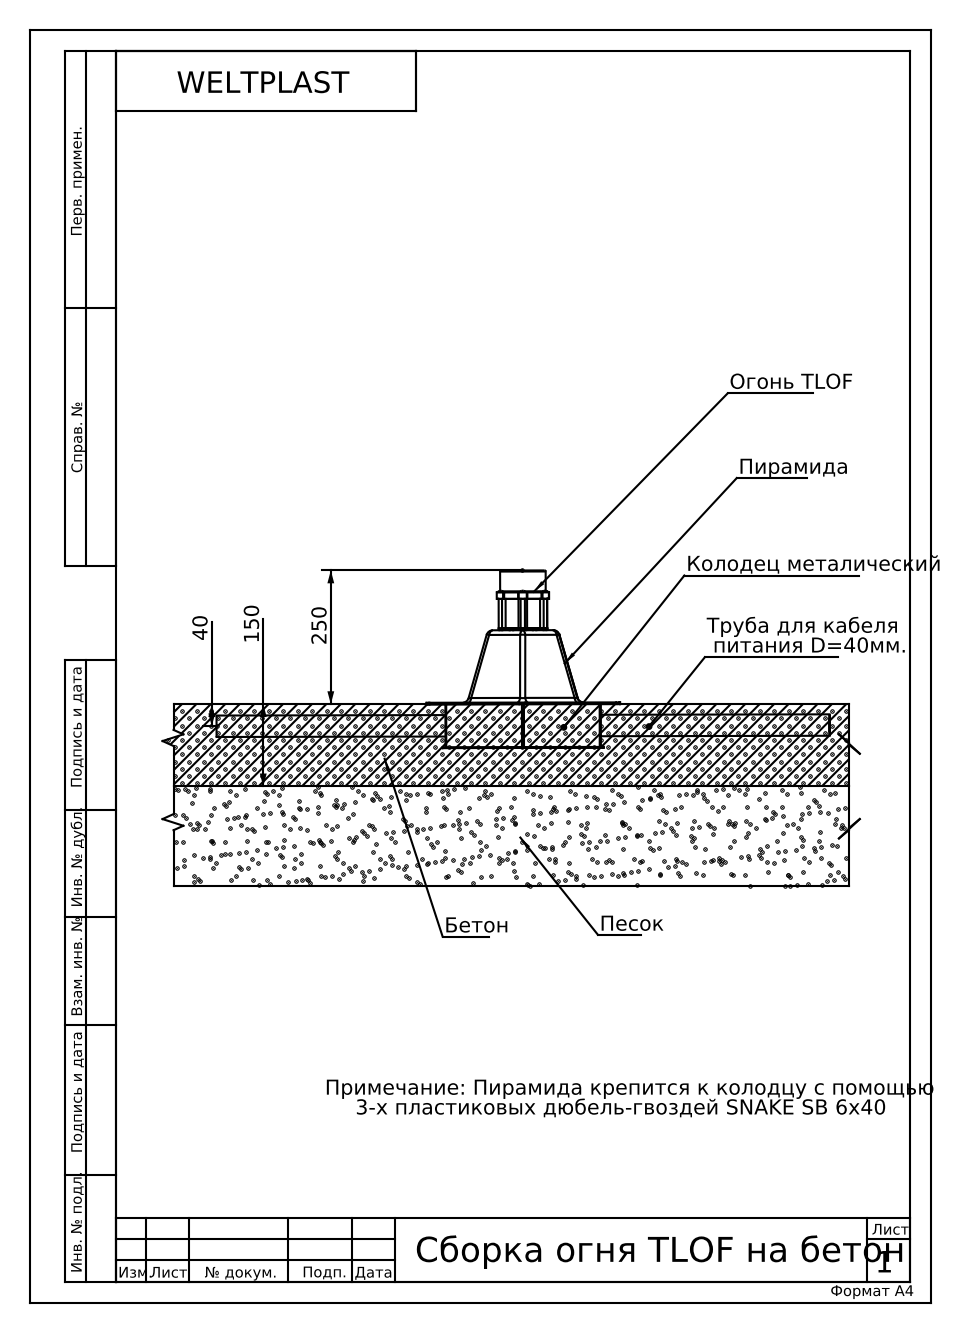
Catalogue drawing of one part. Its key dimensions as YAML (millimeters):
part_name: "конектор зажим; конектор мама защёлка; Сборка на бетон; socket button head cap screw_am_B18.3.4M - 4 x 0.7 x 16 SBHCS --N (+8 more)"
step_written_by: "SolidWorks 2018 (AUTOMOTIVE_DESIGN)"
units: millimeters
bodies: {solids: 40, faces: 1507, planar: 620, cylindrical: 669, other: 218}
overall_size: [1013.06, 601.51, 331]
volume: 1709000
surface_area: 1006000
round_holes:
  - {diameter: 4.4, count: 7}
  - {diameter: 4.5, count: 6}
  - {diameter: 5, count: 5}
  - {diameter: 5.3, count: 4}
  - {diameter: 4, count: 3}
  - {diameter: 4.2, count: 2}
  - {diameter: 12.6, count: 2}
  - {diameter: 20.25, count: 2}
  - {diameter: 26, count: 2}
  - {diameter: 40, count: 2}
  - {diameter: 12, count: 1}
  - {diameter: 70, count: 1}
round_bosses_or_shafts:
  - {diameter: 7.6, count: 6}
  - {diameter: 5, count: 3}
  - {diameter: 4, count: 3}
  - {diameter: 40, count: 2}
  - {diameter: 21.5, count: 2}
  - {diameter: 19.7, count: 2}
  - {diameter: 15, count: 2}
  - {diameter: 85, count: 1}
partial_cylinders:
  - {radius: 2, count: 28}
  - {radius: 12, count: 26}
  - {radius: 5, count: 24}
  - {radius: 4.5, count: 18}
  - {radius: 1.5, count: 14}
  - {radius: 1, count: 13}
  - {radius: 3, count: 12}
  - {radius: 10, count: 12}
face_to_face_distances: [3, 1.5, 81.5, 80, 84.5, 83, 287.15, 287.48, 286.71, 64.5]
hole_center_spacings: [47.5, 42.28, 54.13, 82.28, 48.09, 55.84, 41.18, 82.27]
